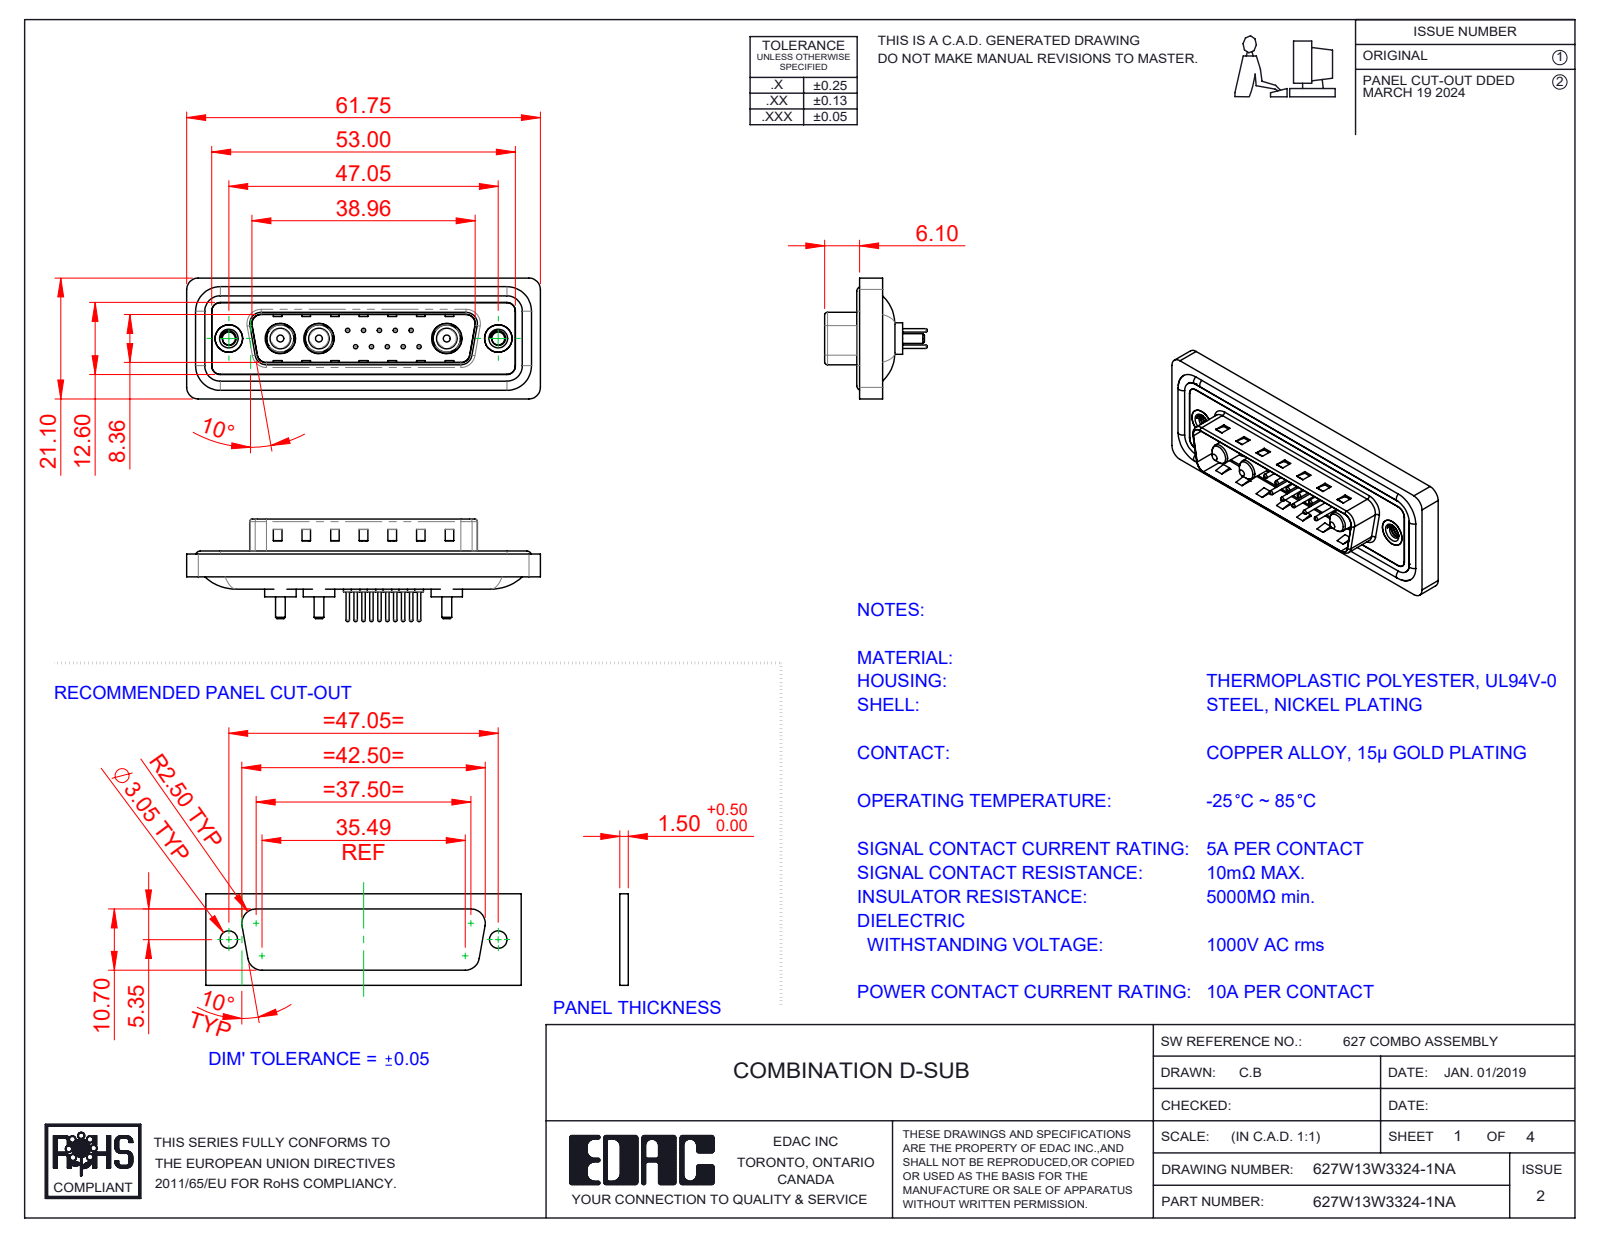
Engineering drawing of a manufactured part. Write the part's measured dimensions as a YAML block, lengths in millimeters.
part_name: "Power Pin_10A S; 627Combo Contact Row 2_24; 627Combo Shell Rear_25 Contacts; 627Combo Shell Front_25 Contacts (+5 more)"
step_written_by: "SolidWorks 2023 (CONFIG_CONTROL_DESIGN)"
units: millimeters
bodies: {solids: 23, faces: 968, planar: 309, cylindrical: 387, other: 272}
overall_size: [61.75, 21.1, 17.9]
volume: 7293
surface_area: 11834
round_holes:
  - {diameter: 0.75, count: 10}
  - {diameter: 1.6, count: 10}
  - {diameter: 2, count: 10}
  - {diameter: 4.85, count: 3}
  - {diameter: 5.3, count: 3}
  - {diameter: 2.26, count: 2}
  - {diameter: 4, count: 2}
  - {diameter: 4.8, count: 2}
  - {diameter: 5, count: 2}
round_bosses_or_shafts:
  - {diameter: 1.5, count: 10}
  - {diameter: 0.6, count: 10}
  - {diameter: 1.6, count: 4}
  - {diameter: 5.5, count: 3}
  - {diameter: 5.2, count: 3}
  - {diameter: 4.75, count: 3}
  - {diameter: 3.75, count: 3}
  - {diameter: 3.6, count: 3}
partial_cylinders:
  - {radius: 1.5, count: 22}
  - {radius: 2, count: 18}
  - {radius: 0.5, count: 8}
  - {radius: 1.6, count: 8}
  - {radius: 0.25, count: 4}
  - {radius: 0.6, count: 4}
  - {radius: 0.65, count: 4}
  - {radius: 0.9, count: 4}
face_to_face_distances: [0.4, 1.5, 1.1, 1.6, 0.5, 3.1, 2.9, 0.82, 9.58, 4.1]
hole_center_spacings: [3.16, 2.77, 5.04, 5.54, 7.49, 5.03, 8.31, 10.11]
